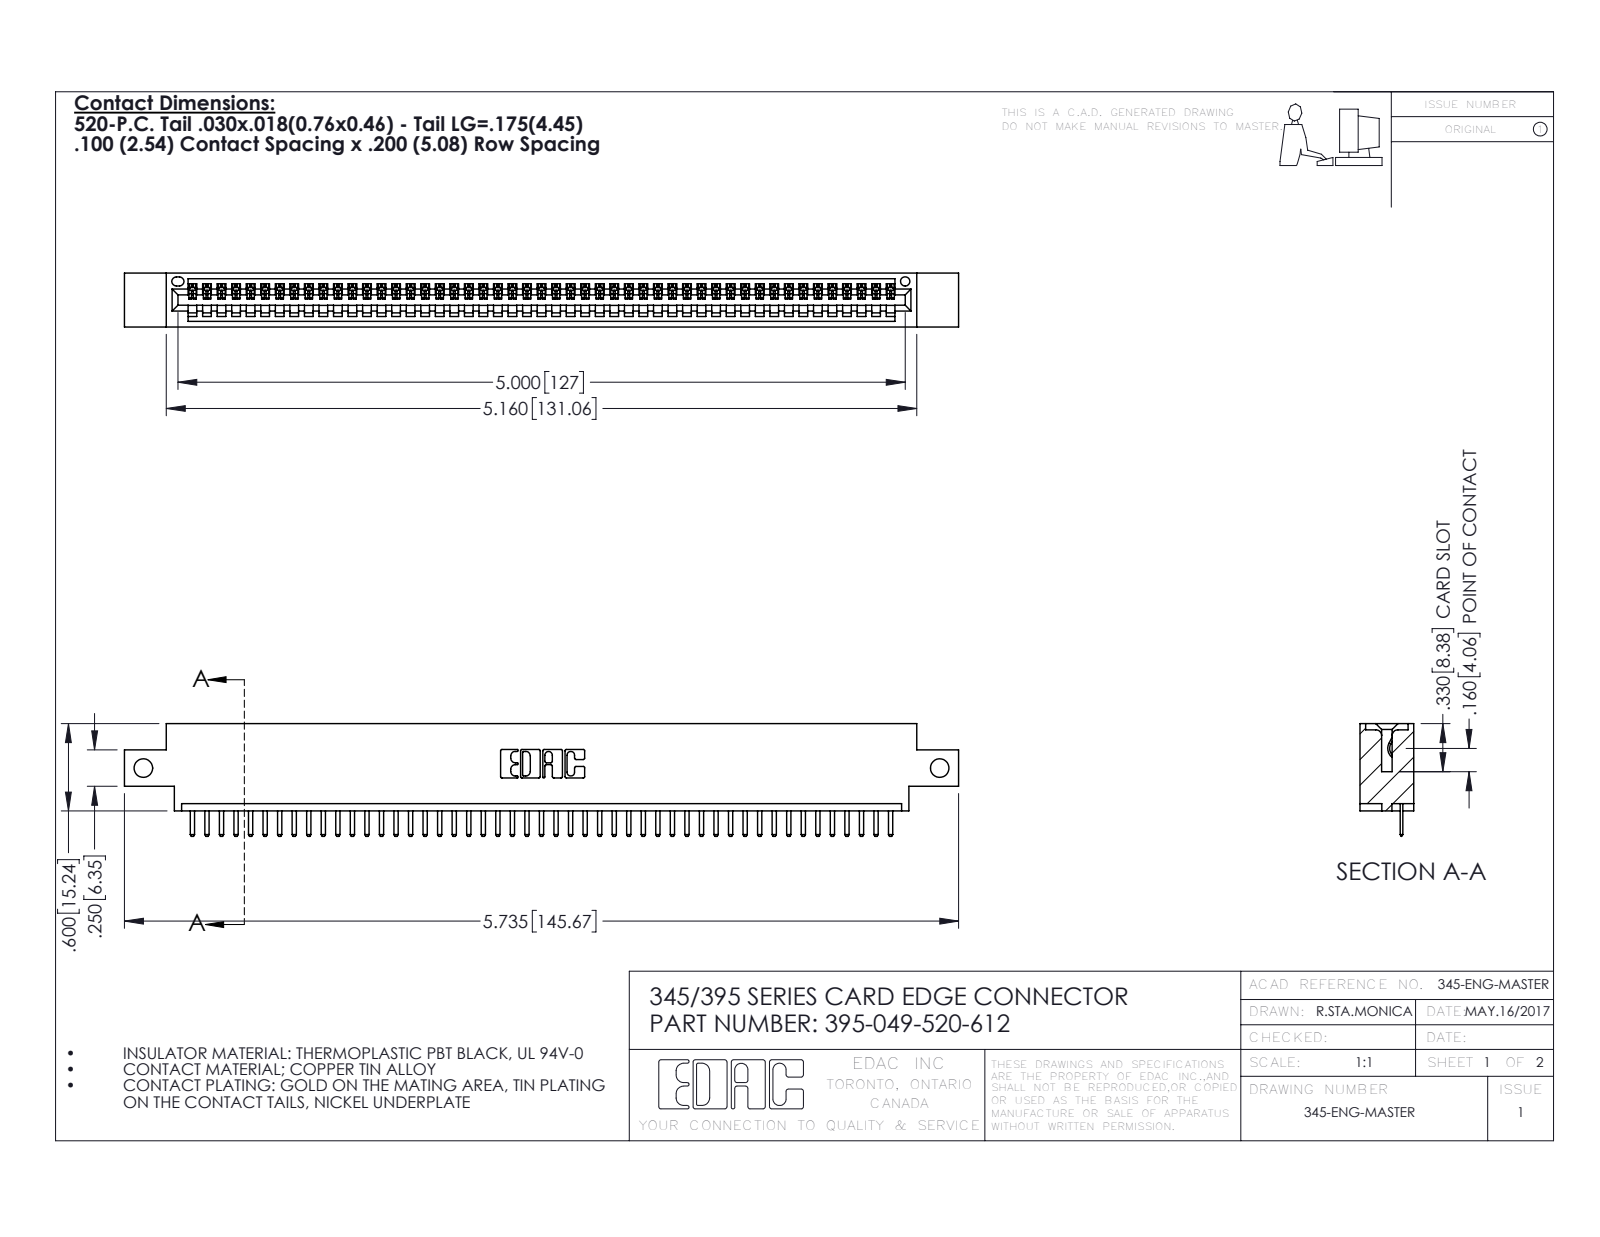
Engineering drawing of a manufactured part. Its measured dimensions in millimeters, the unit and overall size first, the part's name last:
Units: millimetres
Overall size (bounding box): 145.7 × 19.7 × 9.4
Round holes (diameter × count): ⌀3.3 ×2, ⌀1.6 ×1
Partial cylindrical surfaces — rounded edges, fillets, slot ends (radius × count): R0.3 ×100, R0.2 ×98, R0.3 ×22, R0.2 ×6, R0.8 ×6, R0.7 ×3, R0.8 ×2, R1 ×2
Main face-to-face distances: 7.6, 1.8, 9.4, 5.1, 2.5, 6.9, 0.6, 5.7, 1.8, 4.4
Hole centre spacings: 139.1
Volume: 13 600 mm³ · Surface area: 17 630 mm²
Bodies: 50 solids, 3168 faces (2142 planar, 1026 cylindrical, 0 other)
Part name (STEP PRODUCT): 395-049-520-612; 345-292-001_345-293-120; 345 Part_0.170 Offset - Side Mount
STEP written by: SolidWorks 2016 (CONFIG_CONTROL_DESIGN)
